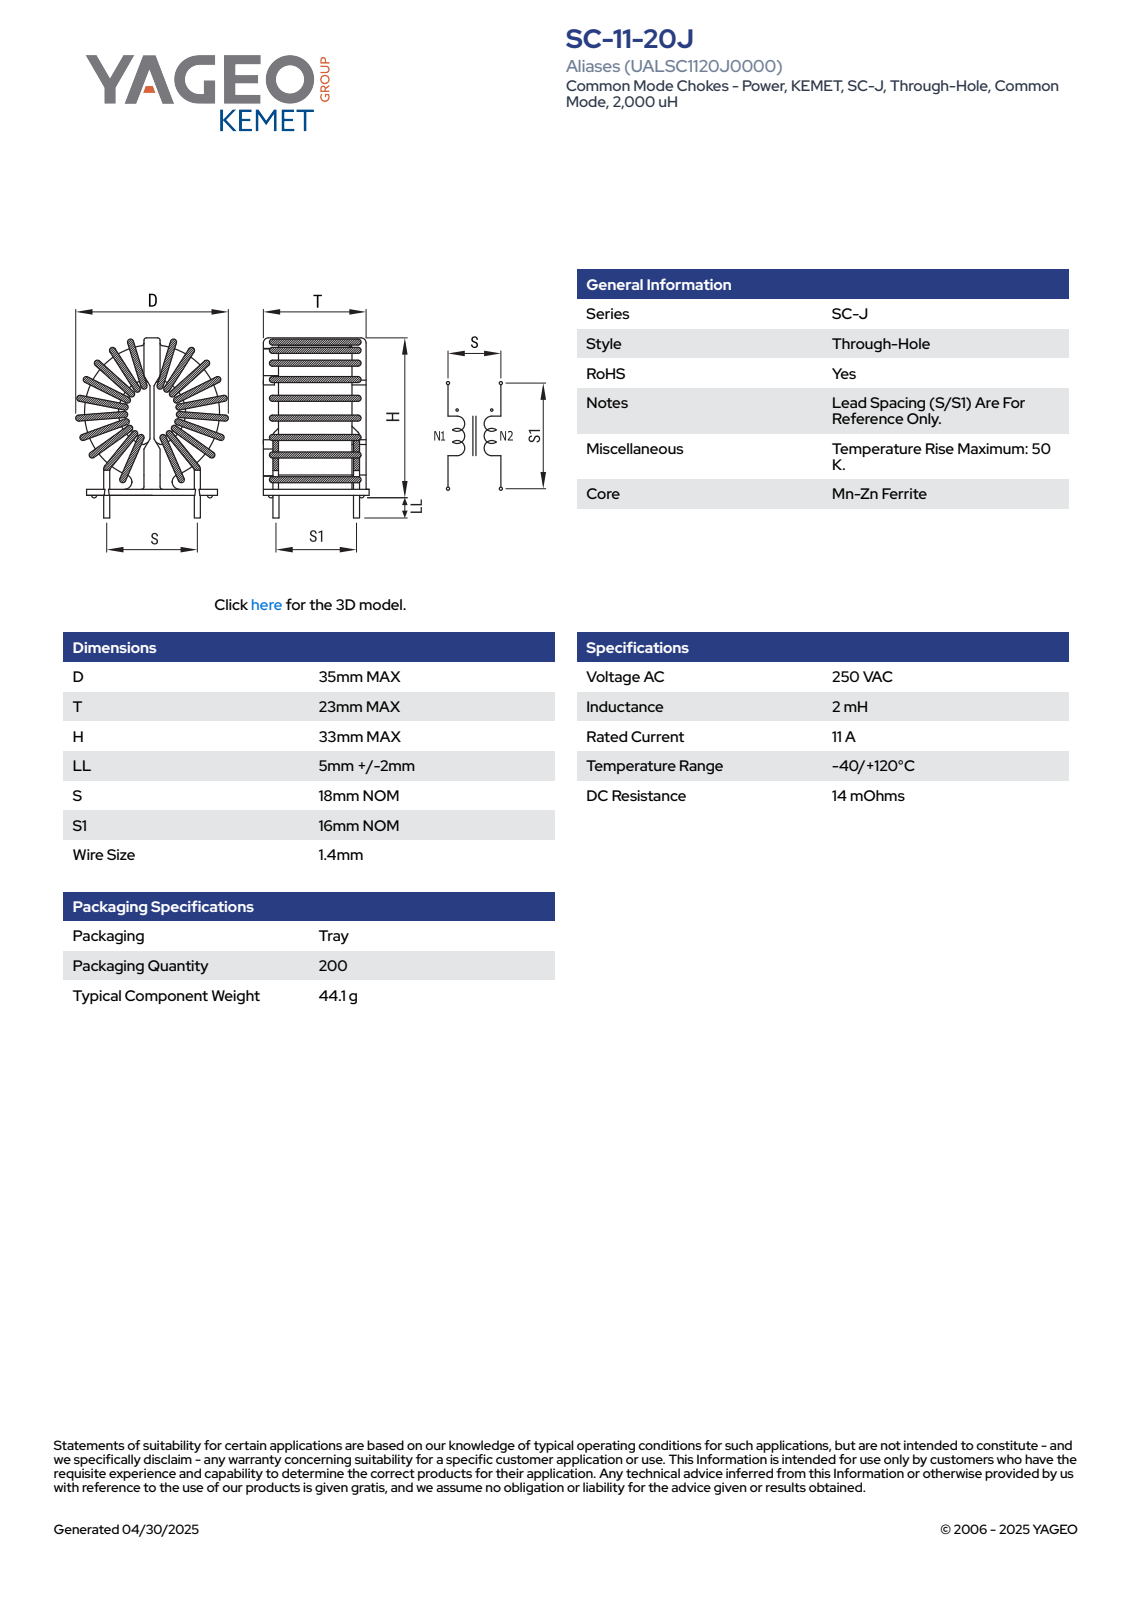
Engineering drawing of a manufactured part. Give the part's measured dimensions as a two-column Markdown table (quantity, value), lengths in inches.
| quantity | value |
| --- | --- |
| part name | SC-11-20J |
| STEP written by | SolidWorks 2018 (CONFIG_CONTROL_DESIGN) |
| units | inches |
| bodies | 2 solids, 358 faces (153 planar, 125 cylindrical, 80 other) |
| overall size | 1.496 × 1.378 × 0.906 |
| volume | 1 in³ |
| surface area | 17.96 in² |
| round holes (diameter × count) | 0.055 × 4, 0.523 × 1, 1 × 1 |
| round bosses / shafts (diameter × count) | 0.055 × 4, 0.039 × 4, 1.056 × 1, 0.992 × 1, 0.579 × 1 |
| partial cylindrical surfaces (radius × count) | 0.02 × 22, 0.028 × 16, 0.039 × 6, 0.059 × 4, 0.177 × 1, 0.285 × 1, 0.295 × 1, 0.492 × 1 |
| main face-to-face distances | 0.661, 0.087, 0.047, 0.031, 0.748, 0.575, 0.118, 0.063, 0.15, 0.598 |
| hole center spacings | 0.63, 0.709, 0.948 |
